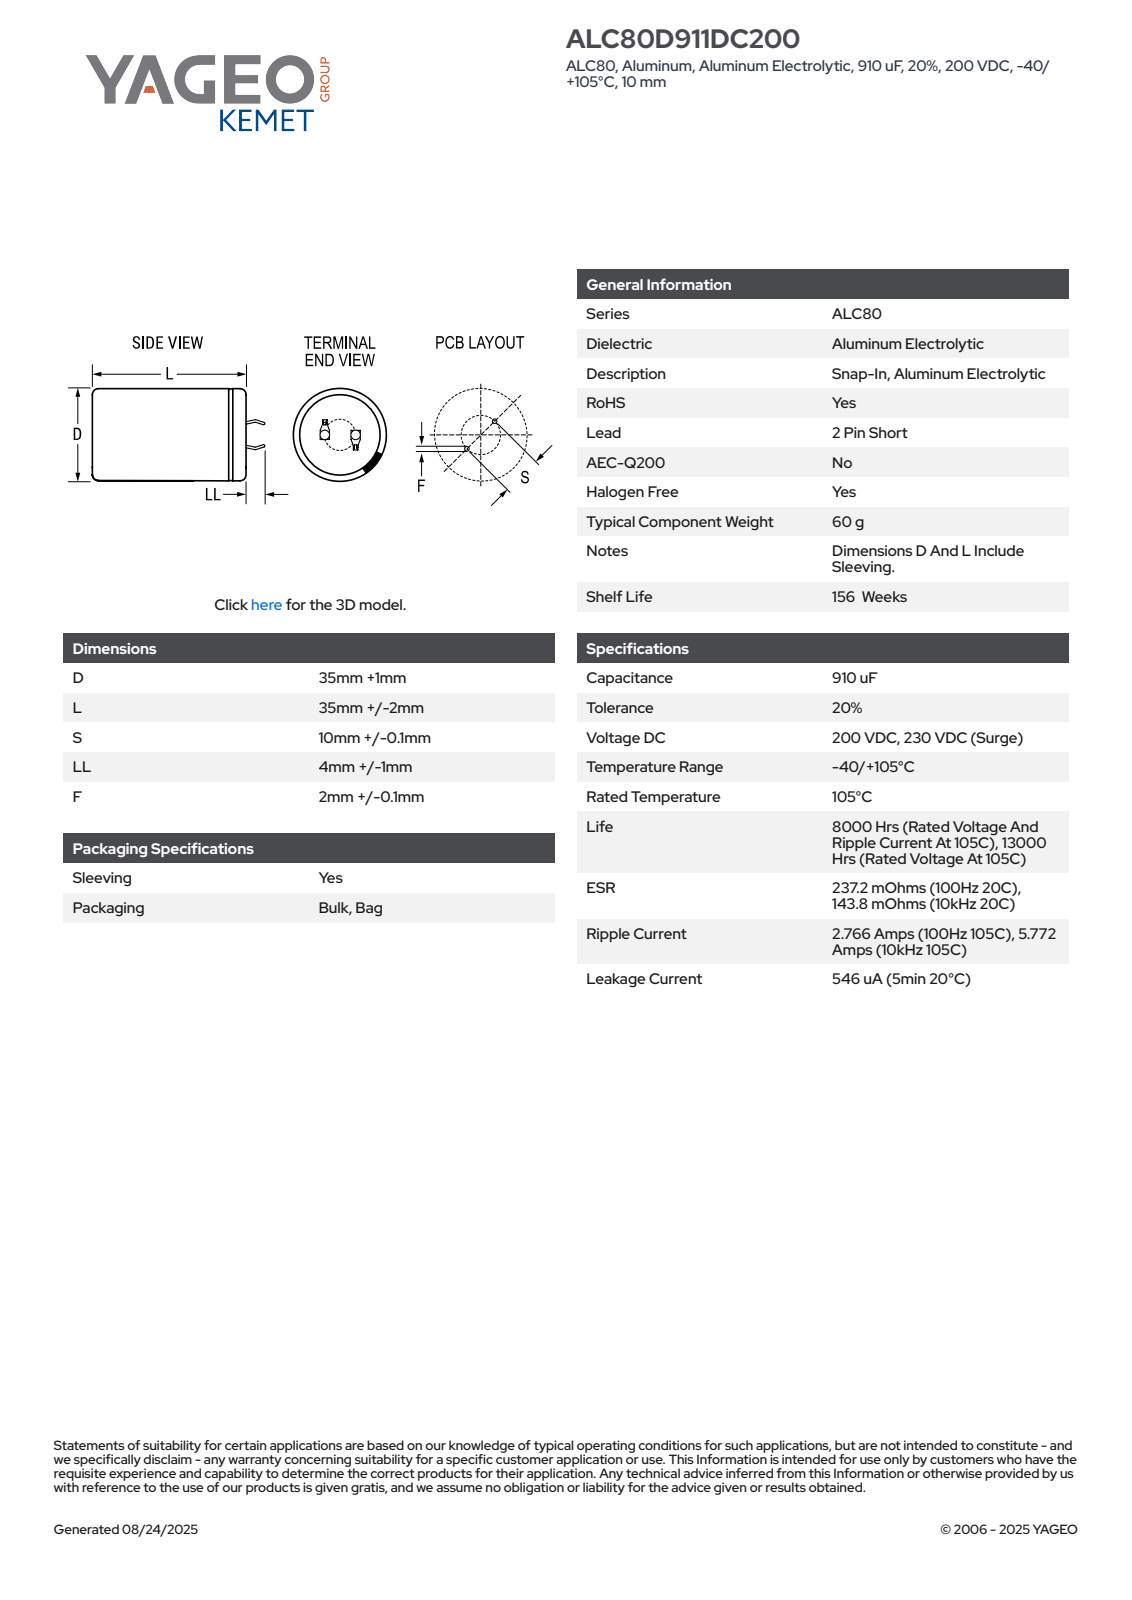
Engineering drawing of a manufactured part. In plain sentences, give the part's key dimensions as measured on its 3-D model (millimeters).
The part is named "CARS_K2P_35X35_D36L37S10LL5F2.1". Its 3-D file was written by "SolidWorks 2014 (AUTOMOTIVE_DESIGN)". It is 1 solid with 100 faces: 52 planar, 9 cylindrical and 39 other. Overall it measures 41.99 by 36 by 36 millimeters. Its volume is 37 132 cubic millimeters and its surface area 6 207 square millimeters. Round holes: 1 of diameter 31.85. Round bosses or shafts: 1 of diameter 36. Partial cylindrical surfaces (rounded edges, fillets, slot ends): 1 of radius 17.99. The main face-to-face distances are 36.99, 37.49, 0.5, 7.08, 0.6, 0.59, 7.6, 0.75, 1.35, 7.68.
